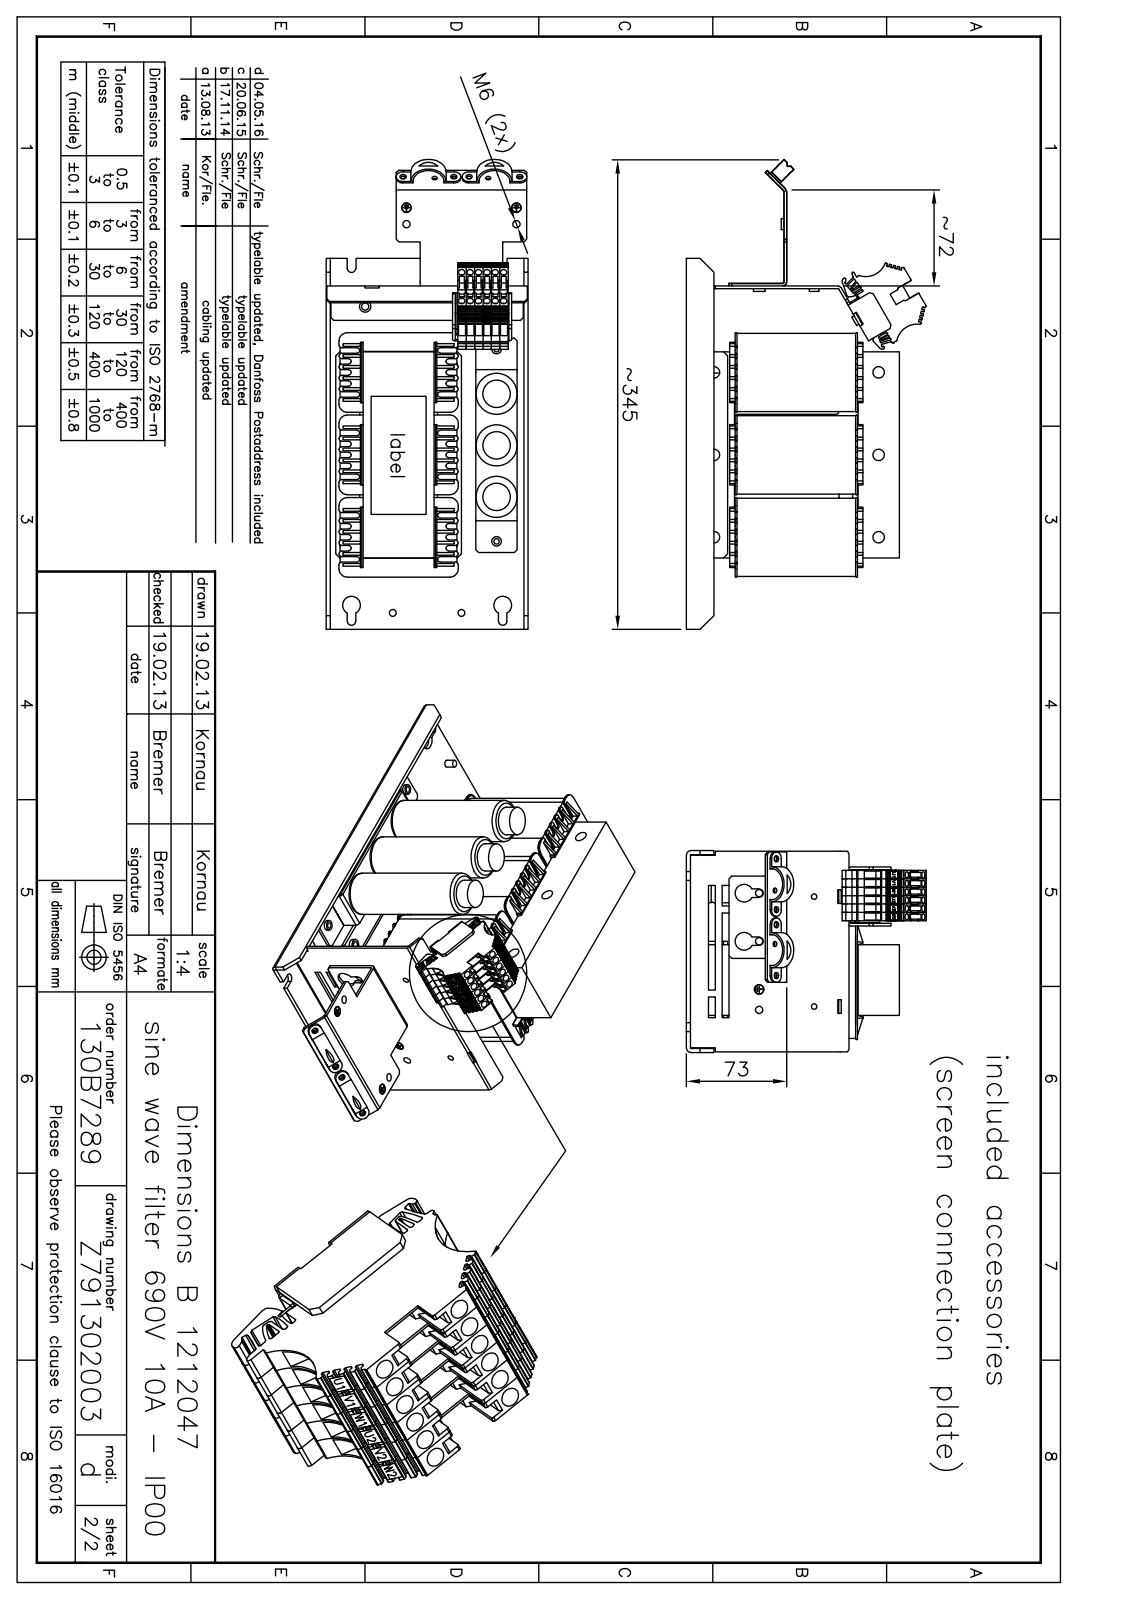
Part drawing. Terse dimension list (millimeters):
name: WDU 4; plain washer grade a_din_Washer DIN 125 - A 4.3; hex nut style 1 gradeab_din_Hexagon Nut ISO 4032 - M5 - D - N; #050-0935 (+8 more)
written by: SolidWorks 2014 (AUTOMOTIVE_DESIGN)
unit: mm
bodies: 96 solids, 4845 faces (2798 planar, 1374 cylindrical, 673 other)
size: 342.13 × 174.39 × 147
volume: 2 209 000 mm³; area: 725 207 mm²
holes: 15× ⌀8.5, 12× ⌀4.2, 12× ⌀4.72, 9× ⌀5.5, 8× ⌀5, 8× ⌀5.3, 6× ⌀5.2, 6× ⌀8, 4× ⌀3.7, 4× ⌀4.3, 4× ⌀4.5, 4× ⌀6
bosses: 12× ⌀10, 8× ⌀12, 8× ⌀6, 6× ⌀11.3, 6× ⌀8, 6× ⌀6.2, 4× ⌀9, 4× ⌀7
rounds: 105× R0.5, 68× R2, 36× R0.2, 18× R0.1, 13× R0.1, 13× R20, 12× R6, 9× R2.1
face distances: 60, 1.5, 3, 2, 120, 1, 1.8, 31.8, 3.1, 51.4
hole spacings: 6.1, 24.81, 12.2, 26.97, 37, 48, 130, 11
